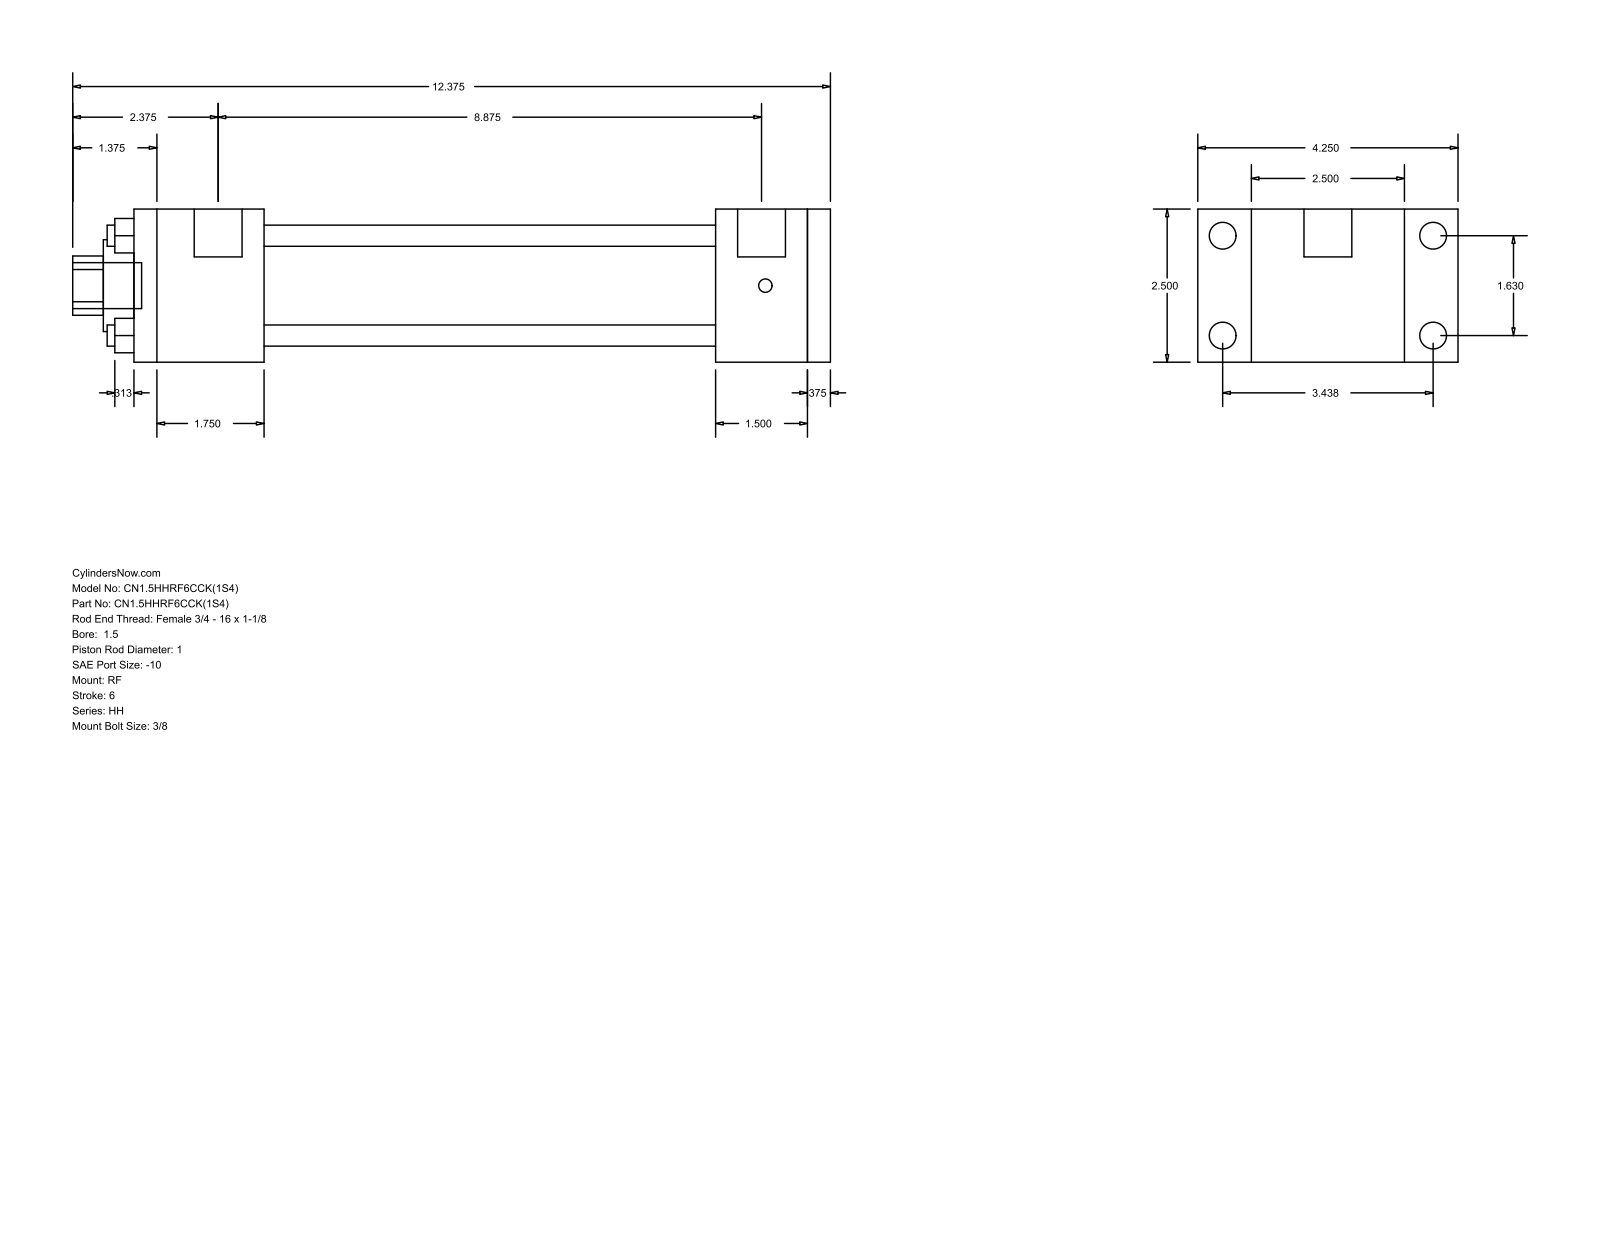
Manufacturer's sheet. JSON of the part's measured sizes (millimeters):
{"part_name": "HH_RF__0150_1", "step_written_by": "GSSL Pune (CONFIG_CONTROL_DESIGN)", "units": "millimeters", "bodies": {"solids": 0, "faces": 92, "planar": 64, "cylindrical": 28, "other": 0}, "overall_size": [314.32, 107.95, 63.5], "round_holes": [[8.76, 4], [25.4, 1], [38.1, 1], [44.45, 1]], "round_bosses_or_shafts": [[11.13, 4], [5.56, 4], [19.84, 2], [19.05, 1]], "partial_cylinders_radius": [[12.29, 1]], "face_to_face_distances": [63.5, 9.52, 187.32, 225.42, 234.94, 38.1, 47.62, 53.98, 241.3, 279.4], "hole_center_spacings": [29.27, 41.4, 58.55]}
